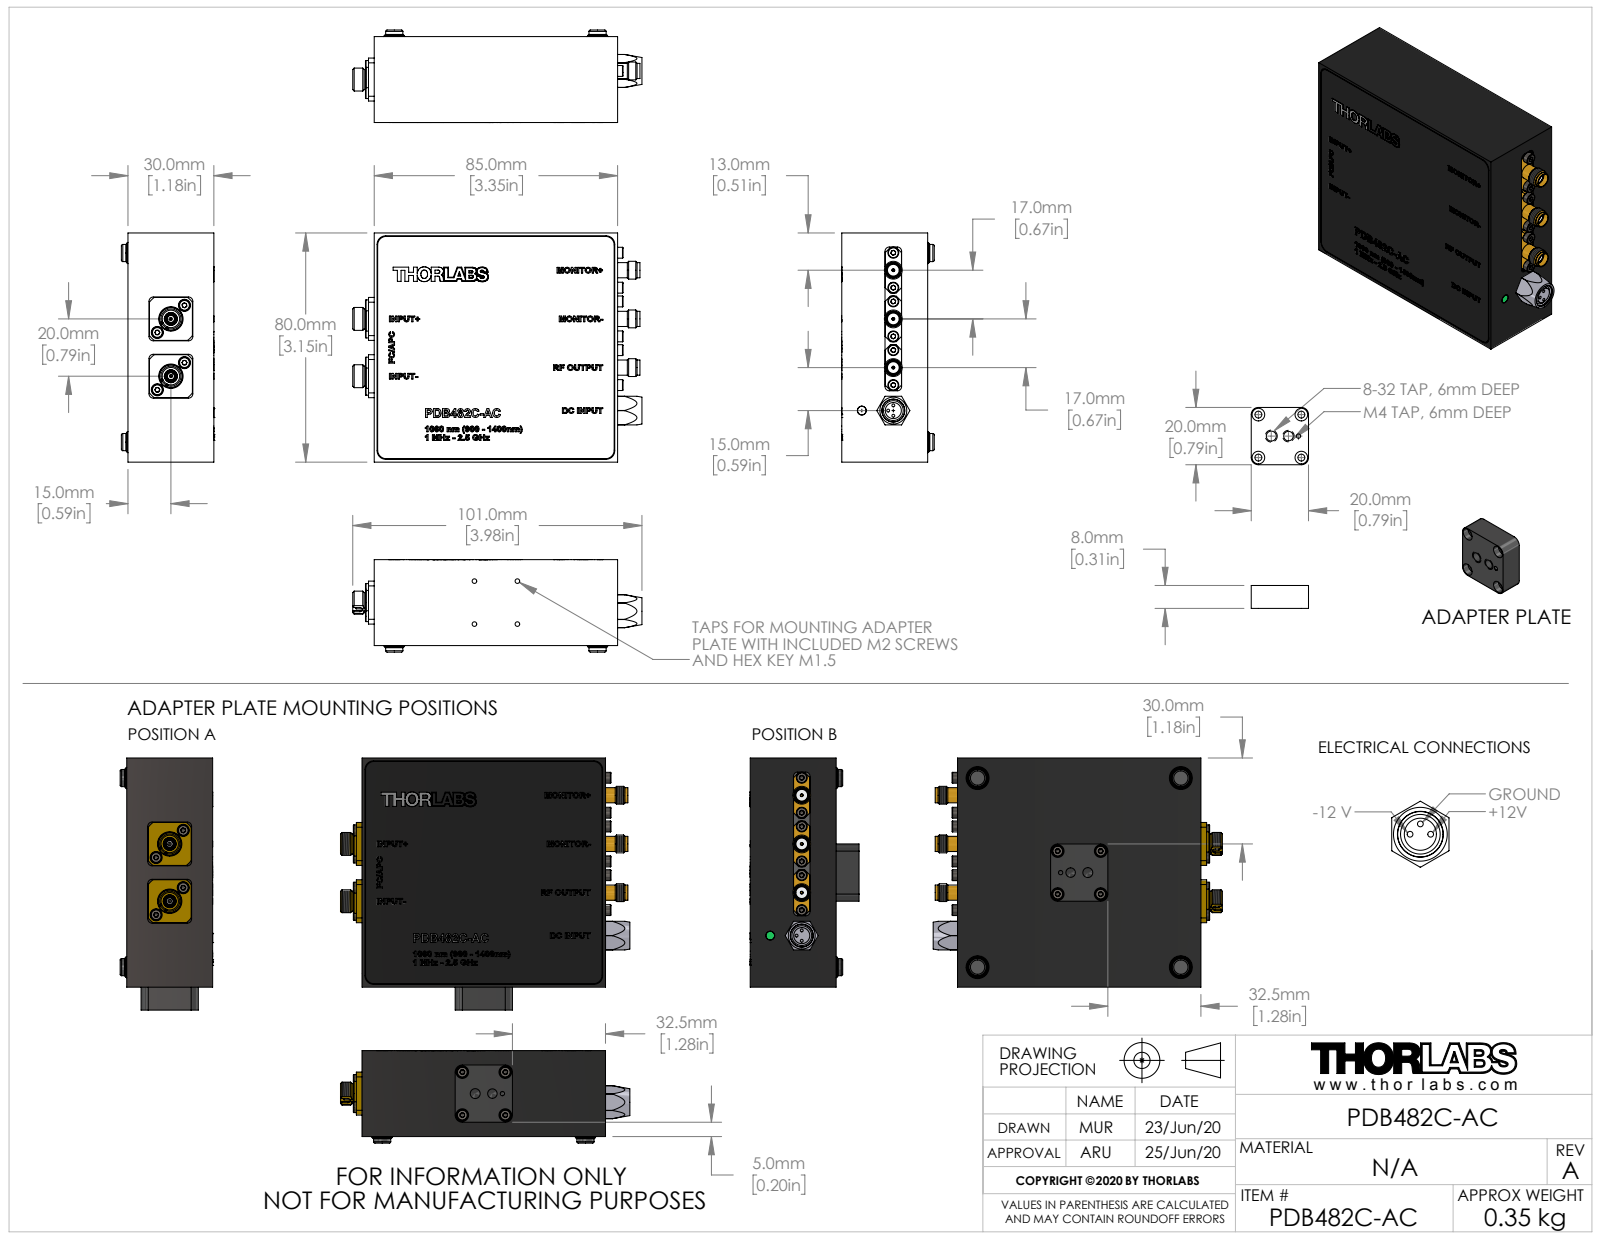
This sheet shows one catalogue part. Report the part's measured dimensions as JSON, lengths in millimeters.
{"part_name": "20.07.10_PDB482C_WEB", "step_written_by": "SolidWorks 2018 (AUTOMOTIVE_DESIGN)", "units": "millimeters", "bodies": {"solids": 0, "faces": 2512, "planar": 1667, "cylindrical": 290, "other": 555}, "overall_size": [101, 88, 32.3], "round_holes": [[1.6, 29], [2.4, 8], [4.4, 8], [2.6, 6], [8, 6], [0.8, 3], [1, 3], [1.5, 3], [4.1, 3], [4.2, 3], [4.7, 3], [3.2, 2]], "round_bosses_or_shafts": [[3.8, 14], [2, 14], [4.2, 8], [2.3, 8], [6, 6], [1.57, 4], [6.22, 3], [5.3, 3]], "partial_cylinders_radius": [[5, 18], [3, 16], [1.5, 12], [1.02, 4], [2.4, 4], [2.5, 4], [8, 3], [9.5, 2]], "face_to_face_distances": [4, 3, 16.7, 19.7, 23.7, 6, 24, 4.3, 30, 25.7], "hole_center_spacings": [15, 6.1, 17, 2.83, 8.75, 10.9, 12.9, 15.05]}
